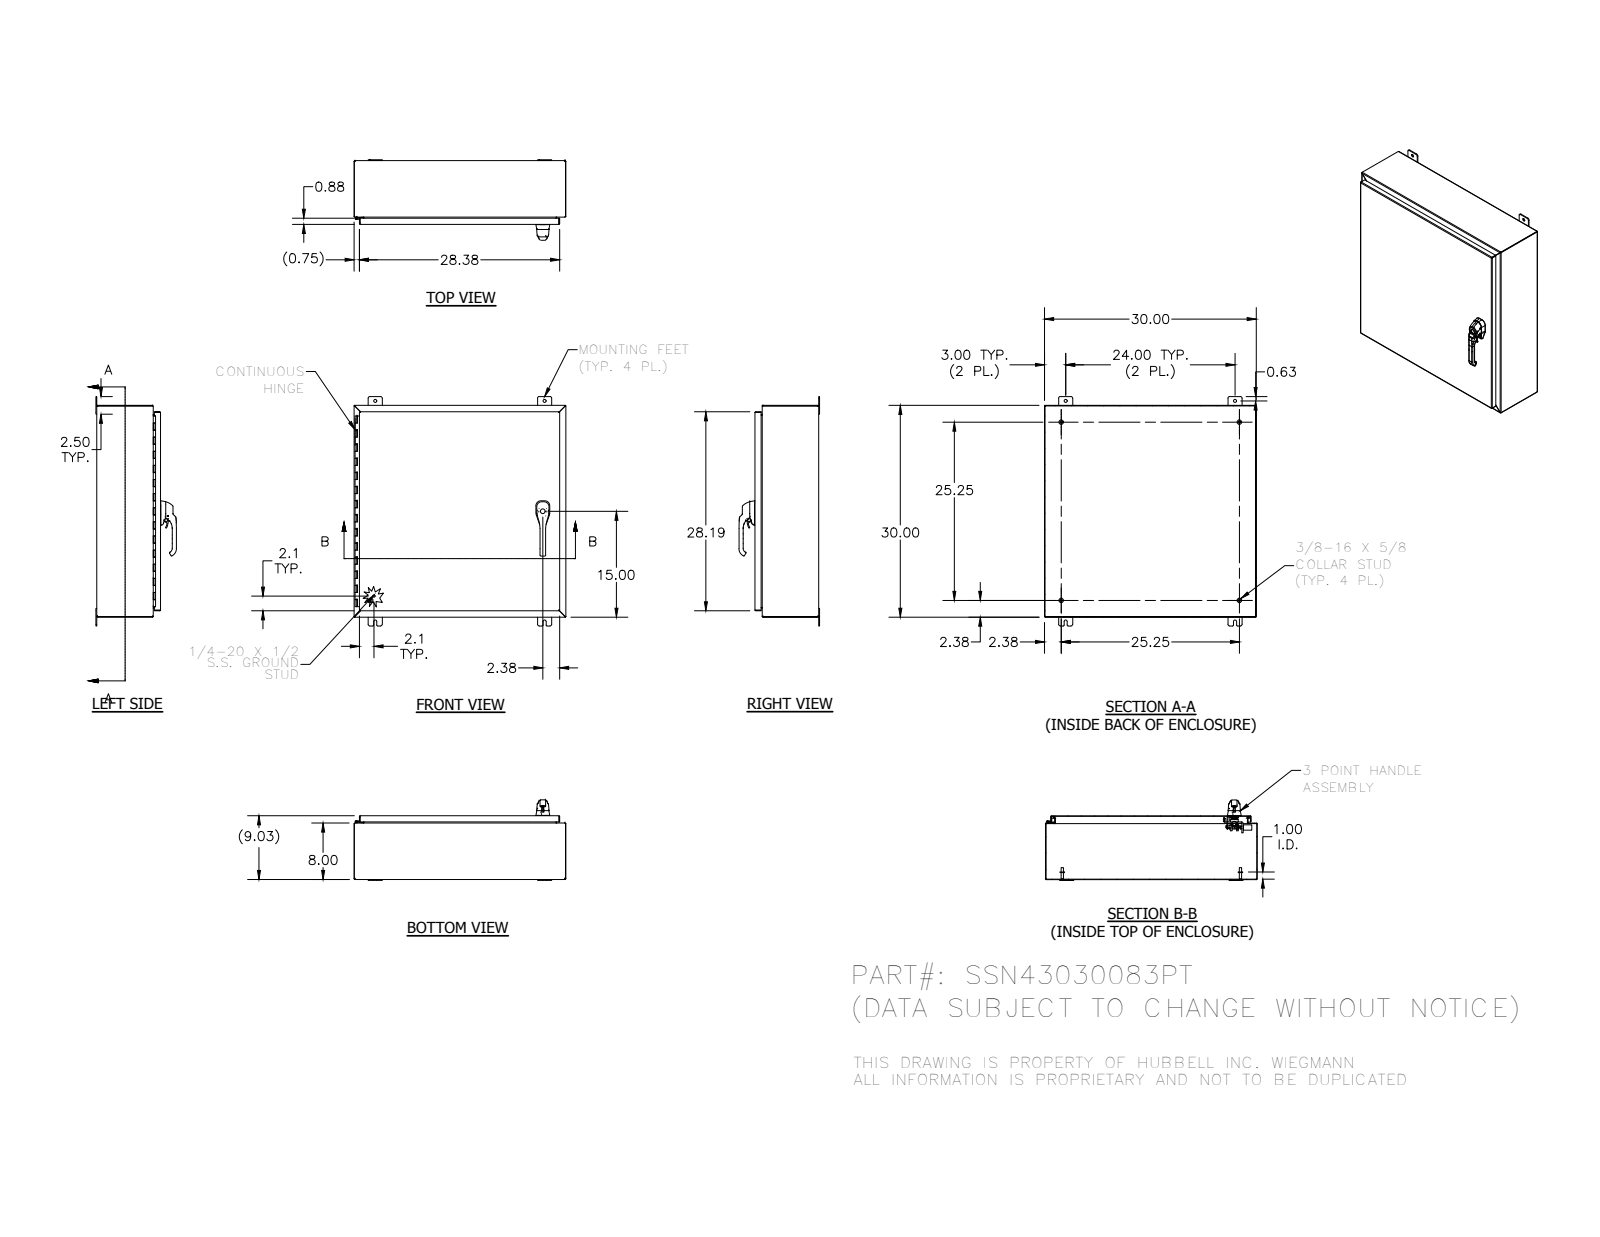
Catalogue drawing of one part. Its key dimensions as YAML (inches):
part_name: "3862; 1091-903_AF0_2; 2100-11; 31230 (+8 more)"
step_written_by: "SolidWorks 2014 (AUTOMOTIVE_DESIGN)"
units: inches
bodies: {solids: 56, faces: 3128, planar: 1047, cylindrical: 1296, other: 785}
overall_size: [32.5, 30, 11.408]
volume: 254
surface_area: 6591
round_holes:
  - {diameter: 0.262, count: 8}
  - {diameter: 0.187, count: 4}
  - {diameter: 0.438, count: 4}
  - {diameter: 0.213, count: 3}
  - {diameter: 0.281, count: 3}
  - {diameter: 0.241, count: 2}
  - {diameter: 0.25, count: 2}
  - {diameter: 0.252, count: 2}
  - {diameter: 0.315, count: 2}
  - {diameter: 0.4, count: 2}
  - {diameter: 0.402, count: 2}
  - {diameter: 0.413, count: 2}
round_bosses_or_shafts:
  - {diameter: 0.625, count: 4}
  - {diameter: 0.33, count: 4}
  - {diameter: 0.236, count: 3}
  - {diameter: 1, count: 2}
  - {diameter: 0.563, count: 2}
  - {diameter: 0.533, count: 2}
  - {diameter: 0.531, count: 2}
  - {diameter: 0.5, count: 2}
partial_cylinders:
  - {radius: 0.02, count: 172}
  - {radius: 0.012, count: 113}
  - {radius: 0.125, count: 26}
  - {radius: 0.031, count: 24}
  - {radius: 0.019, count: 21}
  - {radius: 0.105, count: 20}
  - {radius: 0.25, count: 20}
  - {radius: 0.025, count: 16}
face_to_face_distances: [0.074, 8.959, 29.926, 8.885, 9.033, 29.852, 30, 7.926, 1.033, 8]
hole_center_spacings: [0.38, 0.492, 0.76, 0.886, 20.428, 0.234, 0.258, 0.38]
